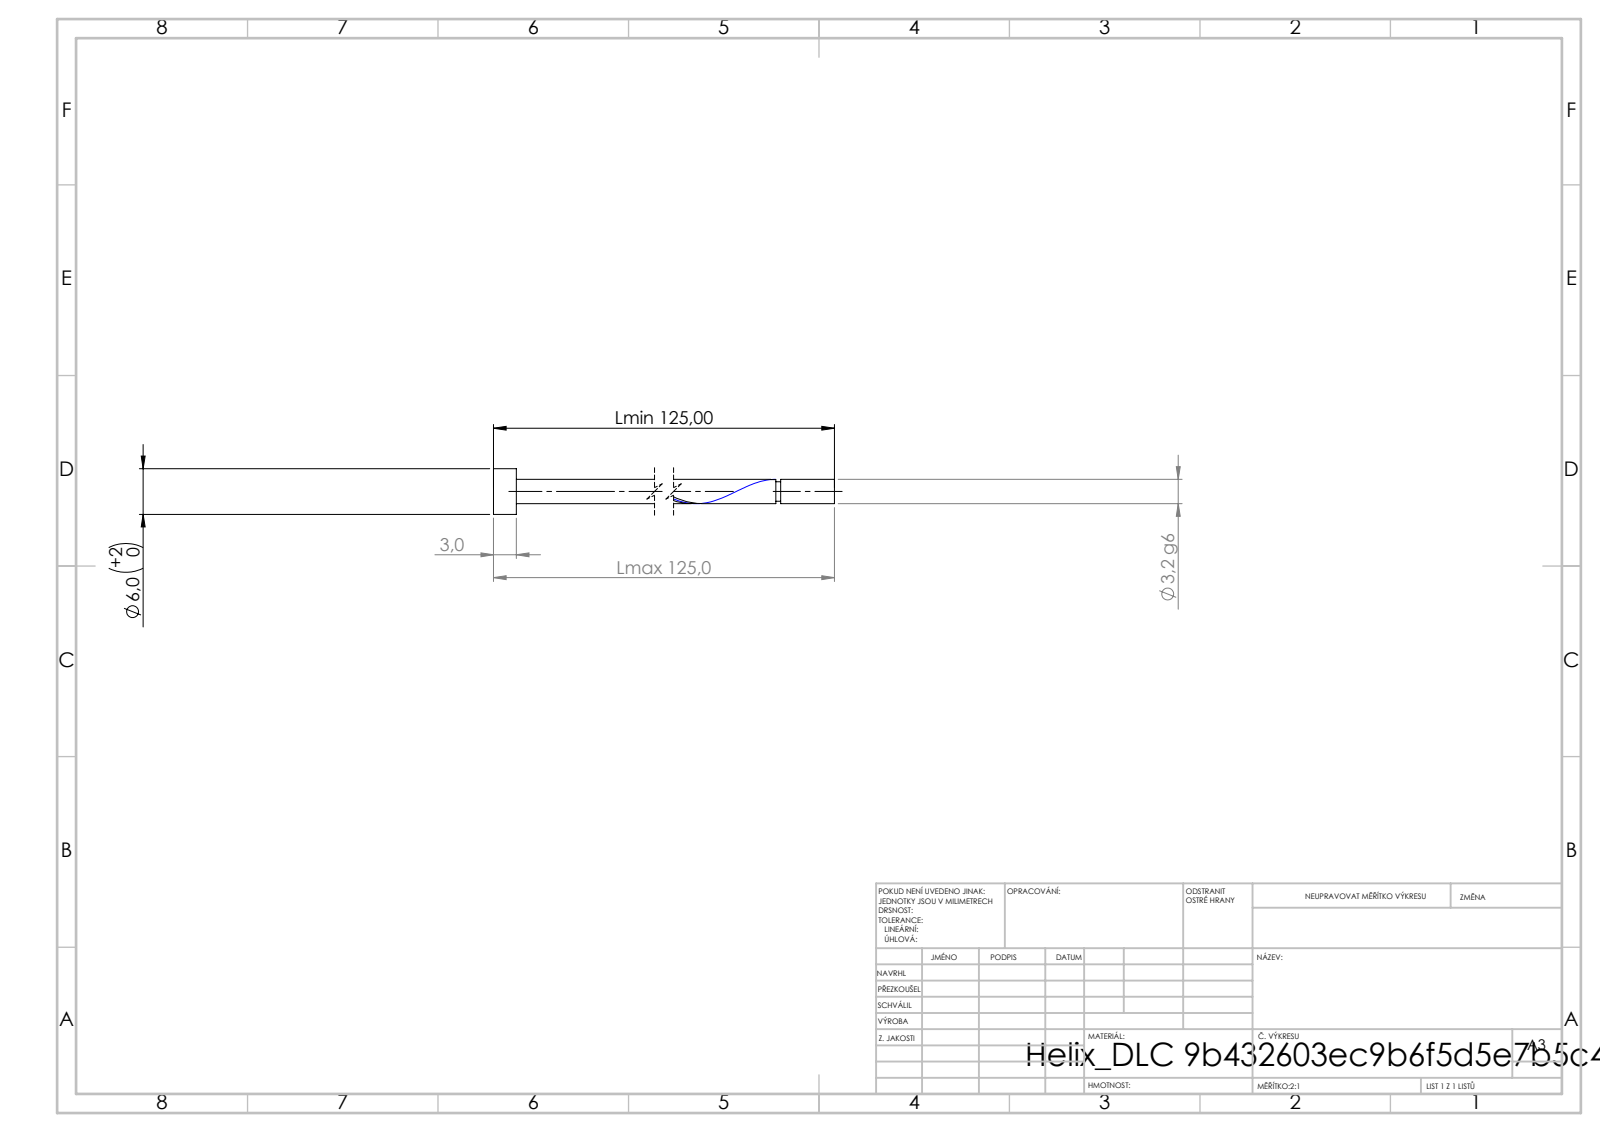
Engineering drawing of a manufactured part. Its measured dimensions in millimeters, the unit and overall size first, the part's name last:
Units: millimetres
Overall size (bounding box): 125 × 6 × 6
Round bosses / shafts (diameter × count): ⌀6 ×1, ⌀3.2 ×1, ⌀2.56 ×1
Main face-to-face distances: 3, 125, 122, 117.95, 114.95, 7.05, 117.31, 114.31, 0.64, 7.69
Volume: 1 055 mm³ · Surface area: 1 366 mm²
Bodies: 1 solid, 21 faces (6 planar, 14 cylindrical, 1 other)
STEP written by: SolidWorks 2019 (CONFIG_CONTROL_DESIGN)
